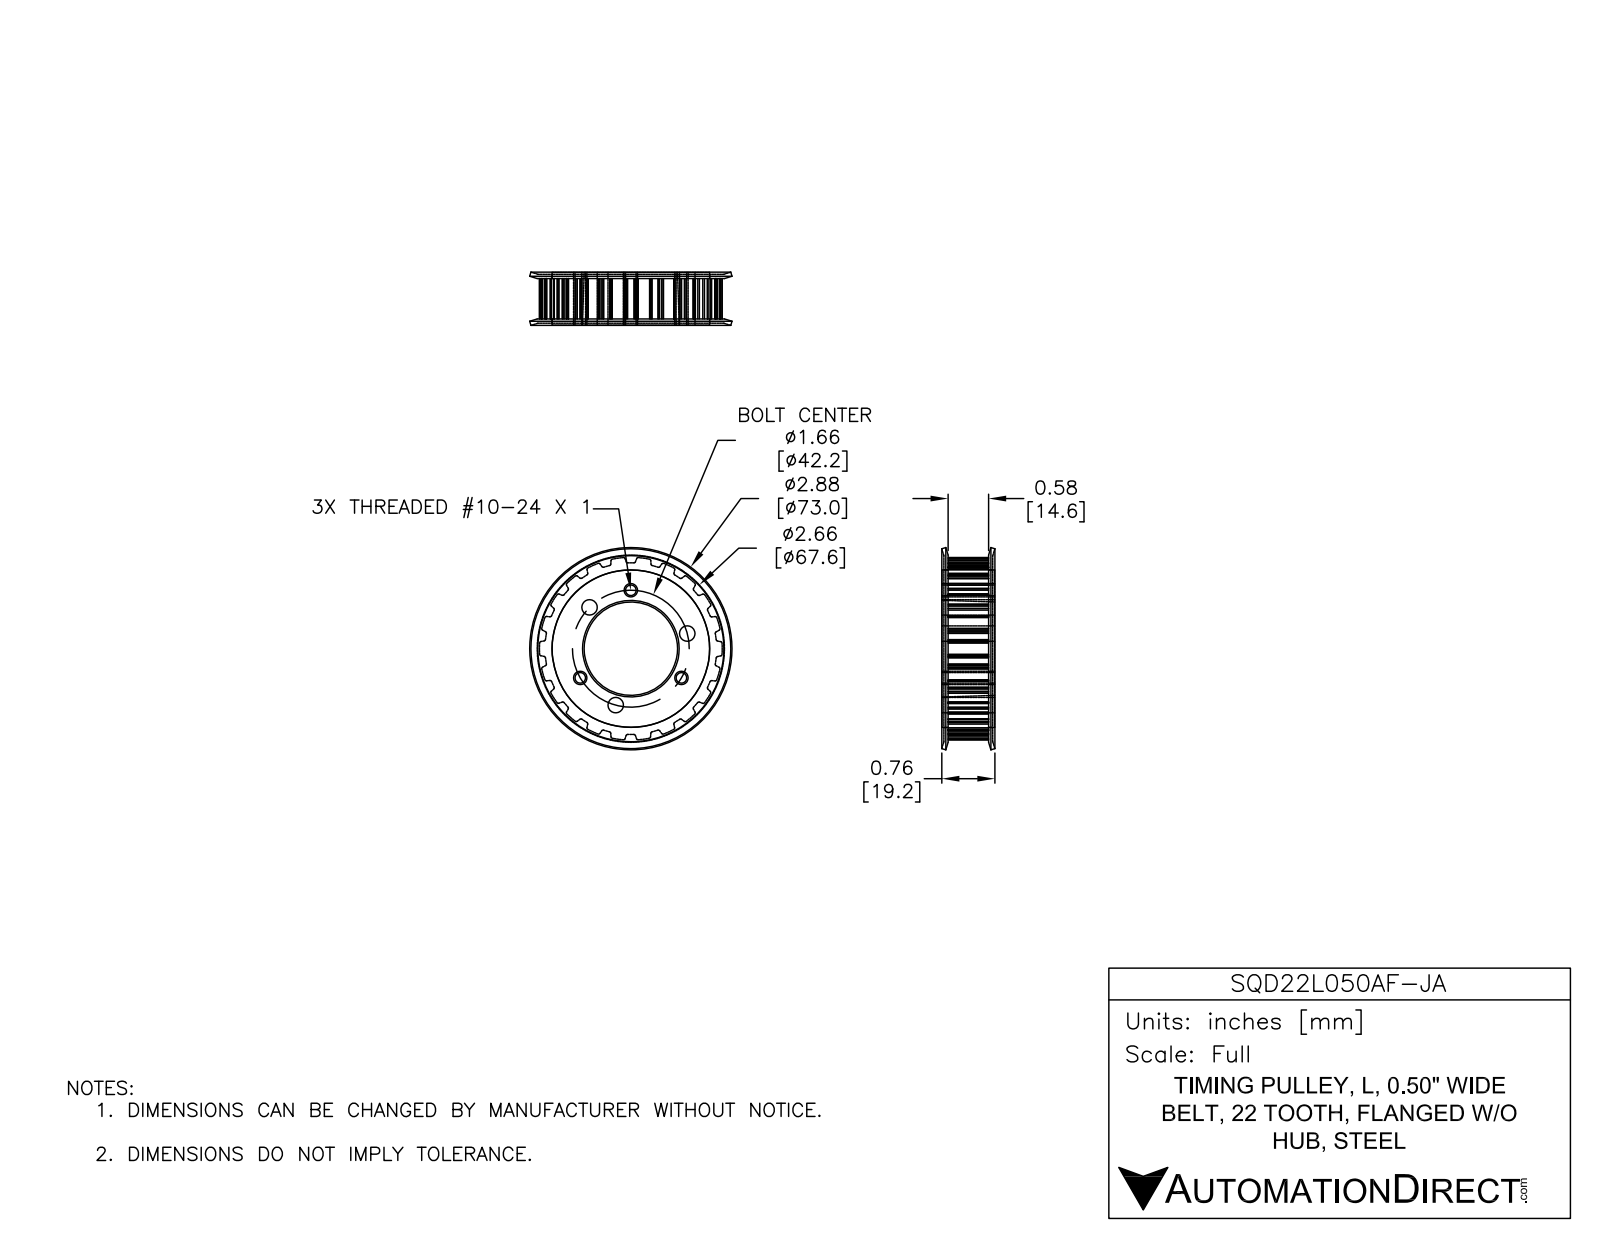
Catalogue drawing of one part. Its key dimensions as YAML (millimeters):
part_name: "SQD22L050AF-JA"
step_written_by: "SolidWorks 2018 (AUTOMOTIVE_DESIGN)"
units: millimeters
bodies: {solids: 2, faces: 235, planar: 73, cylindrical: 148, other: 14}
overall_size: [73, 73, 19.2]
volume: 41620
surface_area: 22740
round_holes:
  - {diameter: 3.8, count: 3}
  - {diameter: 5.6, count: 3}
  - {diameter: 47.6, count: 1}
  - {diameter: 56.9, count: 1}
round_bosses_or_shafts:
  - {diameter: 56.8, count: 1}
partial_cylinders:
  - {radius: 0.5, count: 88}
  - {radius: 33, count: 1}
face_to_face_distances: [0.7, 18.4, 17.7, 2.5, 15.2, 16, 3.2, 19.1, 2.2, 16.9]
hole_center_spacings: [21.1, 36.5, 36.5, 16.1, 25.7, 41.8, 16.2, 21.1]
